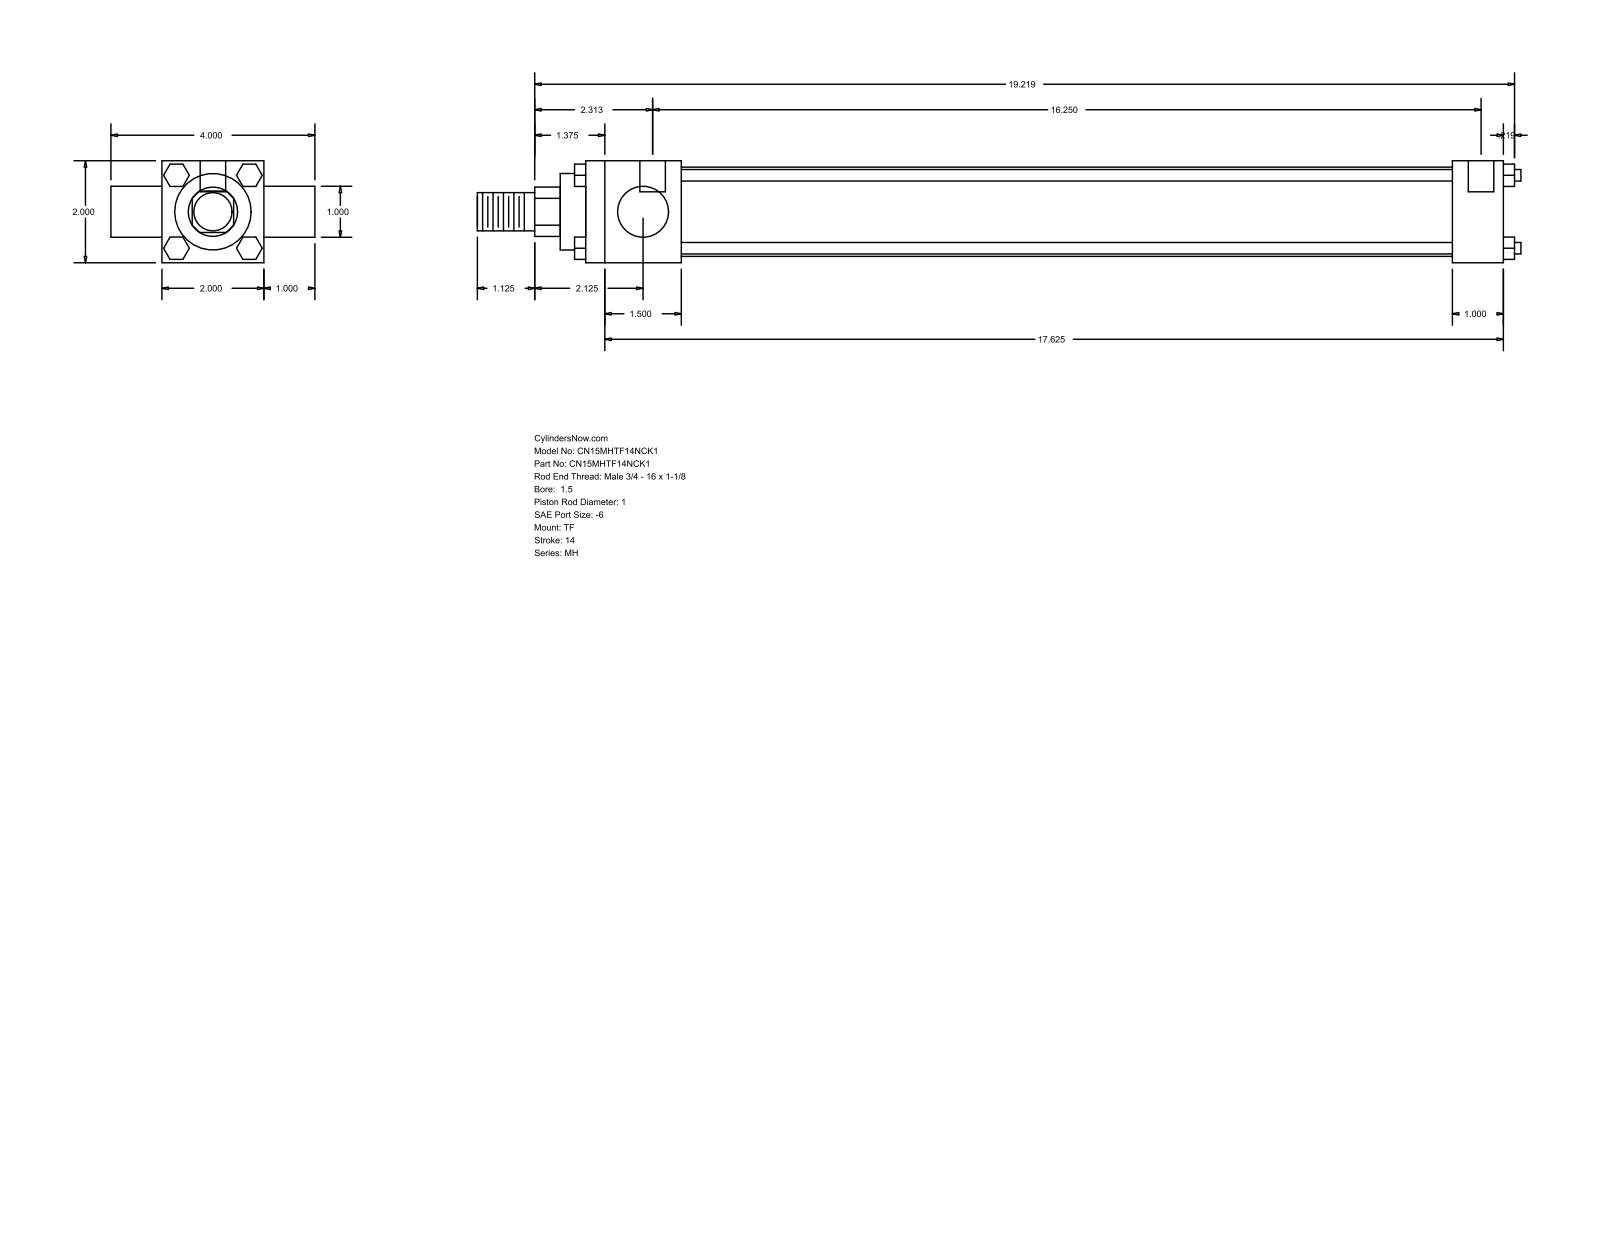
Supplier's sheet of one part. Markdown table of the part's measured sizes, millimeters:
| quantity | value |
| --- | --- |
| part name | MH_TF__0150_1 |
| STEP written by | GSSL Pune (CONFIG_CONTROL_DESIGN) |
| units | millimeters |
| bodies | 0 solids, 120 faces (92 planar, 28 cylindrical, 0 other) |
| overall size | 519.91 × 101.6 × 50.8 |
| round holes (diameter × count) | 5.56 × 3, 12.7 × 2 |
| round bosses / shafts (diameter × count) | 5.71 × 4, 25.4 × 2, 44.45 × 1, 38.1 × 1, 19.05 × 1 |
| partial cylindrical surfaces (radius × count) | 12.29 × 1 |
| main face-to-face distances | 50.8, 25.4, 457.2, 76.2, 47.63, 409.57, 431.8, 384.17, 101.6, 12.7 |
| hole center spacings | 3.18, 412.75, 415.93 |
